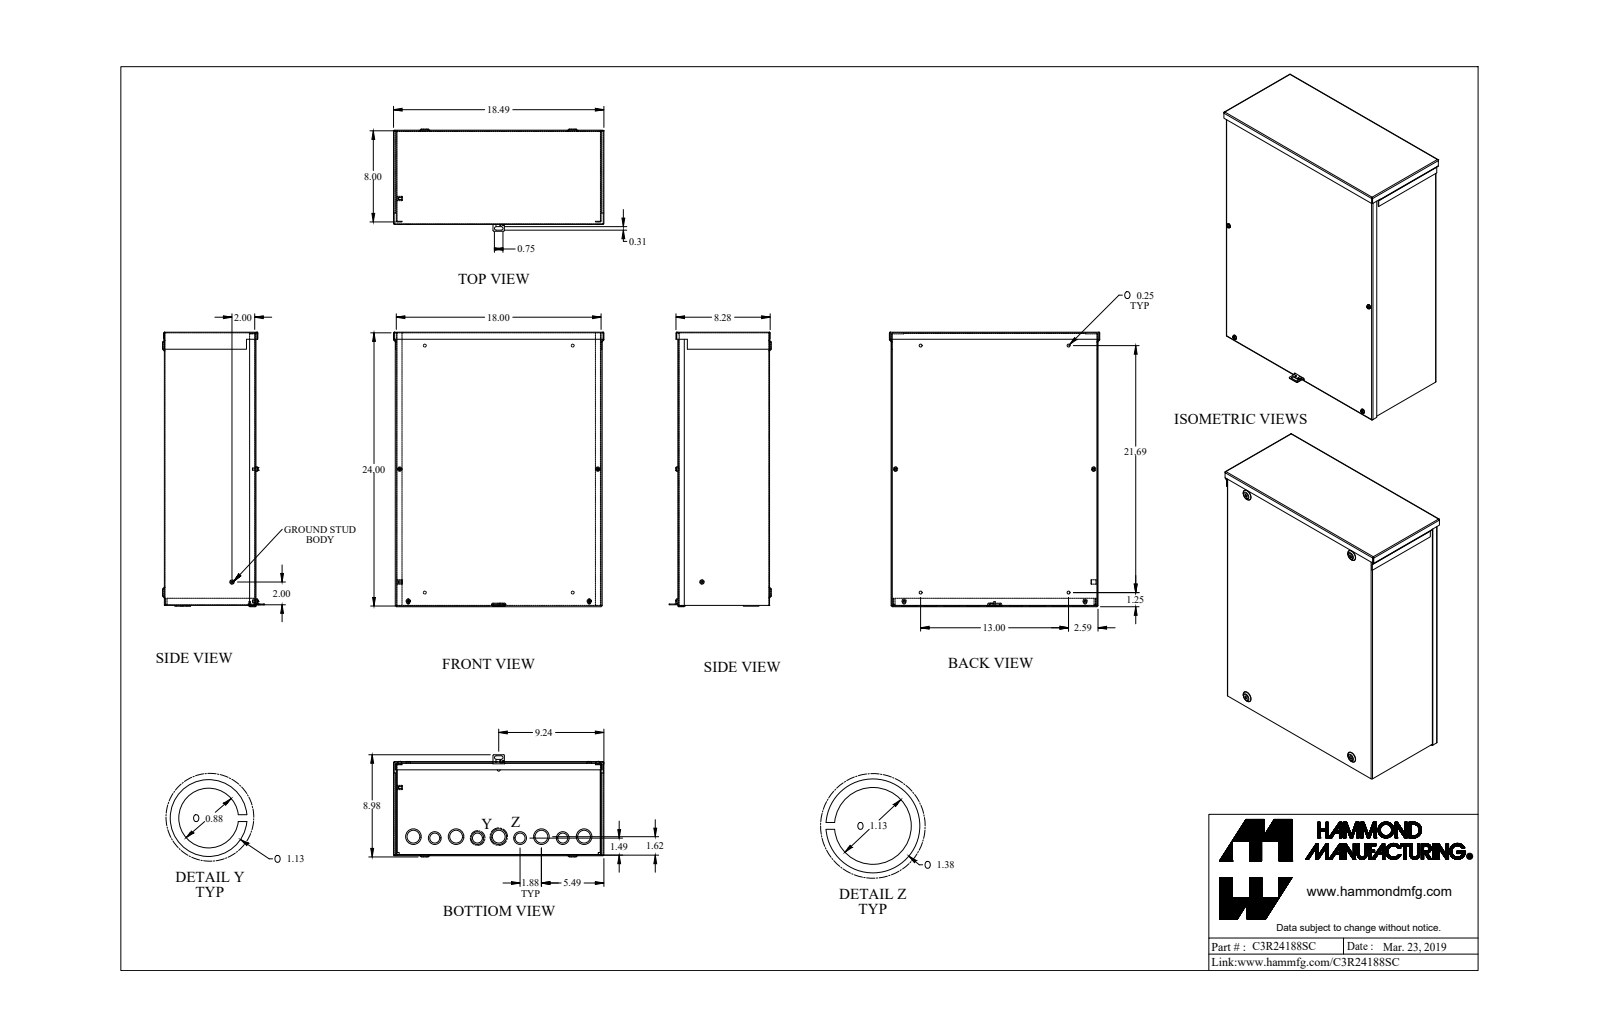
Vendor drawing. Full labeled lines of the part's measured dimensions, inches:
Part name (STEP PRODUCT): C3R24188SC_Default
STEP written by: SolidWorks 2019 (CONFIG_CONTROL_DESIGN)
Units: inches
Bodies: 11 solids, 457 faces (238 planar, 133 cylindrical, 86 other)
Overall size (bounding box): 24.12 × 18.489 × 8.977
Volume: 95.58 in³ · Surface area: 3 367 in²
Round holes (diameter × count): ⌀0.17 ×4, ⌀0.25 ×4, ⌀1.125 ×3, ⌀0.875 ×2, ⌀0.875 ×2, ⌀1.125 ×2, ⌀0.125 ×1, ⌀0.137 ×1, ⌀0.156 ×1
Round bosses / shafts (diameter × count): ⌀1.125 ×4, ⌀0.19 ×4, ⌀1.375 ×3, ⌀0.375 ×3, ⌀1.375 ×2, ⌀0.375 ×2, ⌀0.125 ×1
Partial cylindrical surfaces — rounded edges, fillets, slot ends (radius × count): R0.029 ×21, R0.086 ×21, R0.109 ×8, R0.125 ×8, R0.156 ×2
Main face-to-face distances: 0.057, 8, 7.943, 8.057, 17.943, 18, 0.057, 17.886, 23.886, 23.943
Hole centre spacings: 3.75, 1.879, 1.88, 5.627, 7.5, 11.069, 18.679, 9.376
